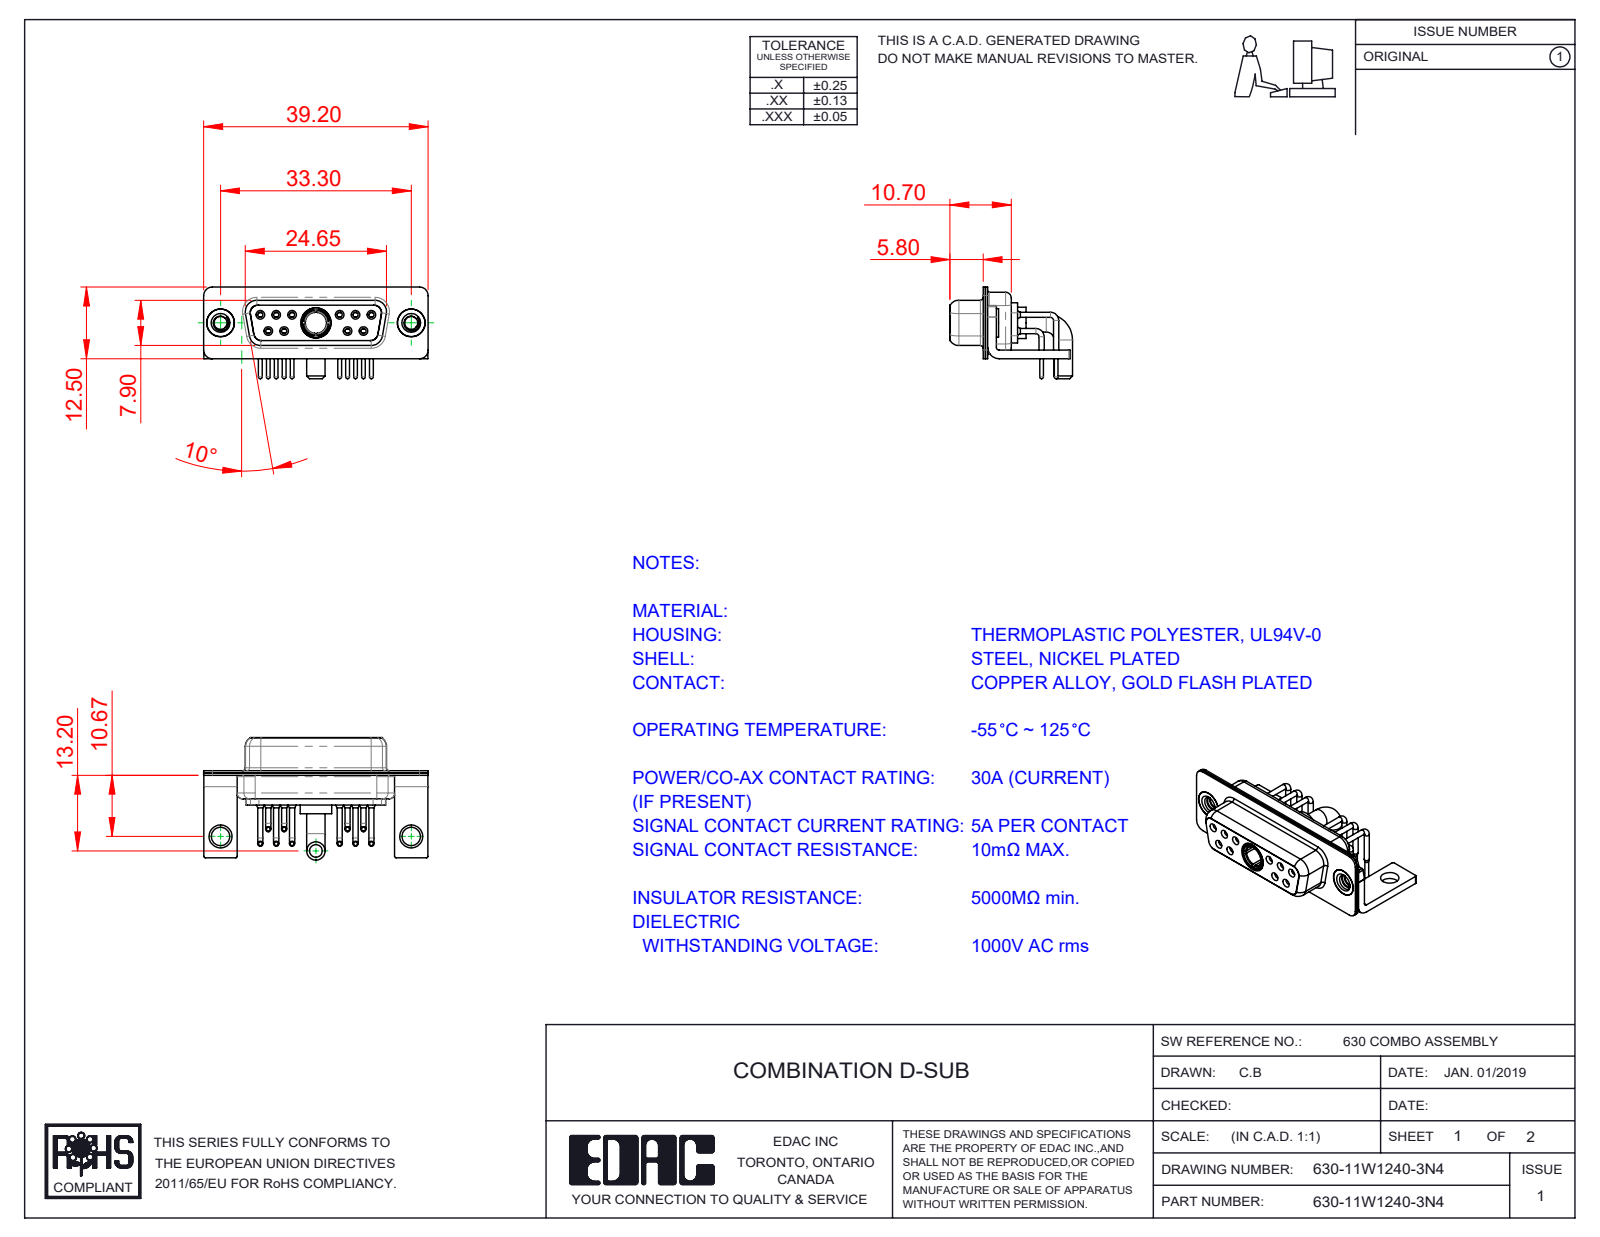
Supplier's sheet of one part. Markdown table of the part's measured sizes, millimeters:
| quantity | value |
| --- | --- |
| part name | 630Combo Stabilizer Bracket; Power Socket_30A RA; 630Combo Contact Row 2; 630Combo Housing_11W1 (+5 more) |
| STEP written by | SolidWorks 2020 (CONFIG_CONTROL_DESIGN) |
| units | millimeters |
| bodies | 19 solids, 927 faces (266 planar, 410 cylindrical, 251 other) |
| overall size | 39.2 × 21.4 × 16 |
| volume | 2 942 mm³ |
| surface area | 6 877 mm² |
| round holes (diameter × count) | 0.9 × 10, 1.1 × 10, 1.5 × 10, 2 × 10, 1.7 × 6, 1.6 × 4, 4.85 × 3, 2.26 × 2, 3.2 × 2, 4 × 2, 4.05 × 2, 3.7 × 1 |
| round bosses / shafts (diameter × count) | 0.9 × 10, 0.65 × 10, 1.6 × 6, 5 × 2, 4.95 × 2, 4.8 × 2, 3.2 × 2, 5.5 × 1 |
| partial cylindrical surfaces (radius × count) | 0.25 × 16, 1.5 × 16, 2 × 13, 1.35 × 12, 1.6 × 8, 0.5 × 5, 0.6 × 4, 0.65 × 4 |
| main face-to-face distances | 0.4, 0.8, 1.4, 0.45, 8.45, 1.5, 1.8, 8.9, 6.2, 2.3 |
| hole center spacings | 3.16, 2.77, 13.85, 11.08, 16.62, 5.03, 5.04, 5.54 |
